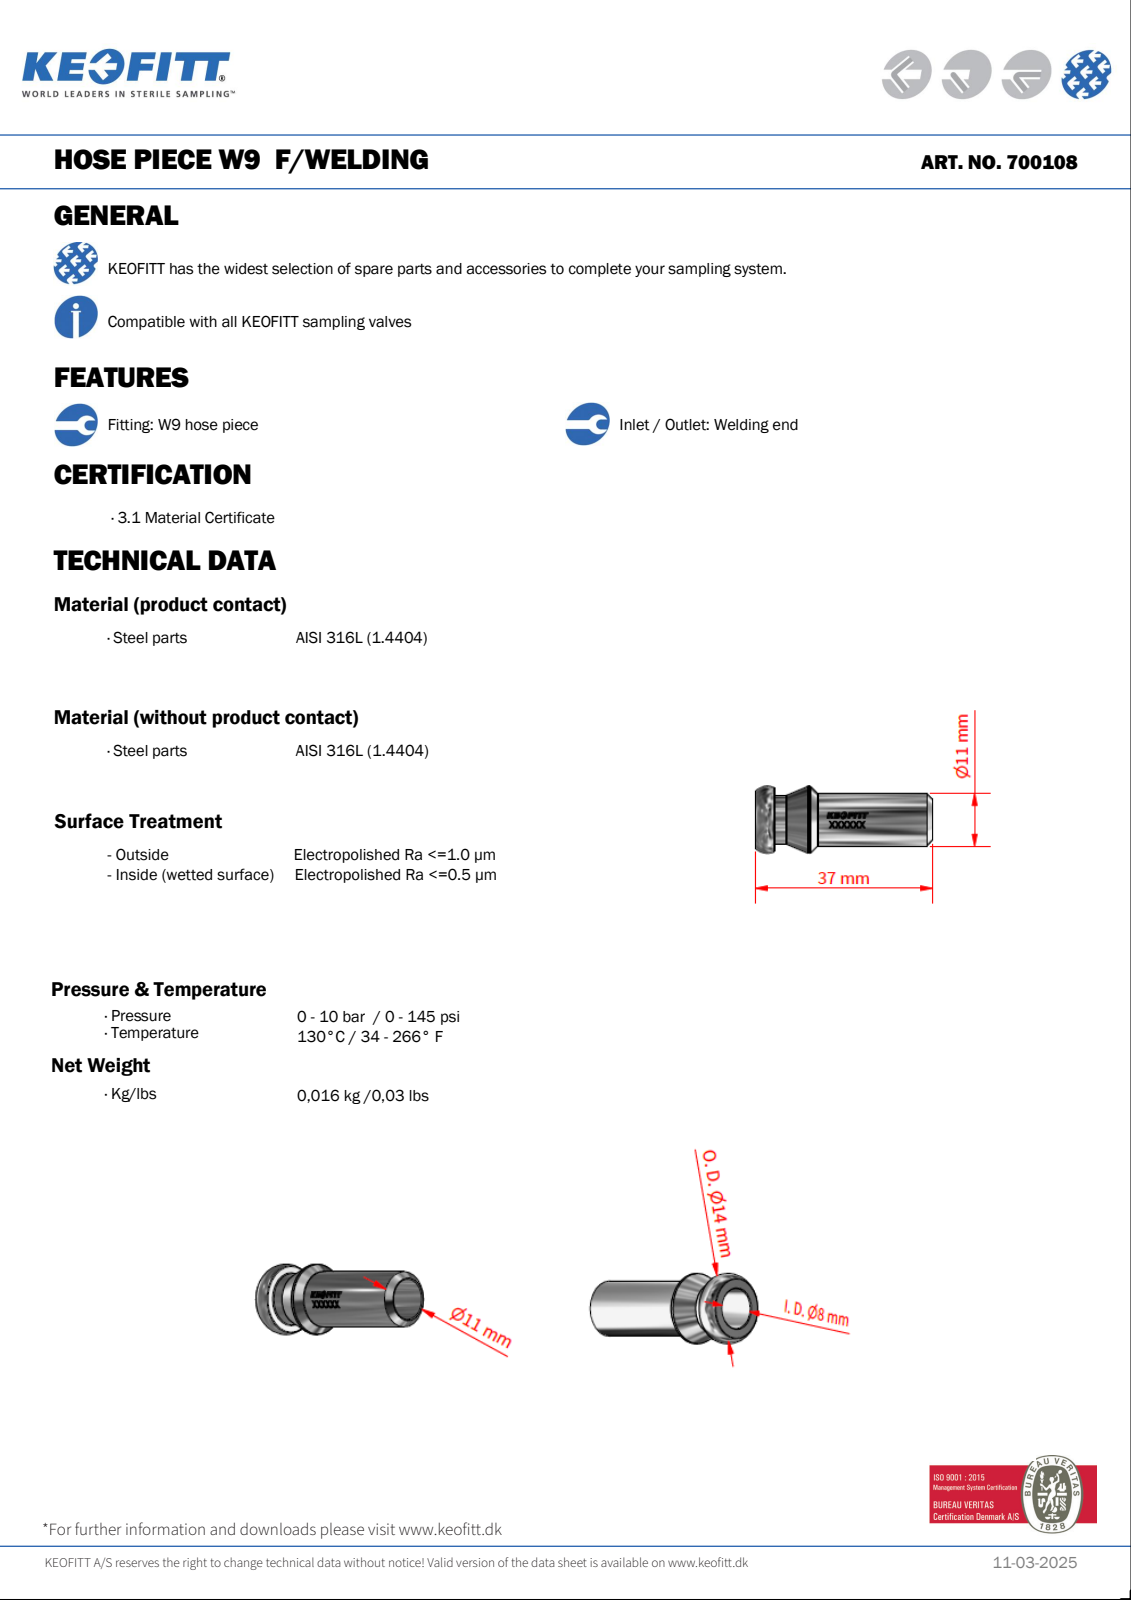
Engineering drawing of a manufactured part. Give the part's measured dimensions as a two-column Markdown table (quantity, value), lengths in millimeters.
| quantity | value |
| --- | --- |
| part name | 700108 |
| STEP written by | Autodesk Inventor 2024 (AUTOMOTIVE_DESIGN) |
| units | millimeters |
| bodies | 1 solid, 17 faces (3 planar, 3 cylindrical, 11 other) |
| overall size | 37 × 14 × 14 |
| volume | 3 821 mm³ |
| surface area | 1 618 mm² |
| round bosses / shafts (diameter × count) | 14 × 1, 11 × 1, 10.2 × 1 |
| main face-to-face distances | 37, 4, 33 |
